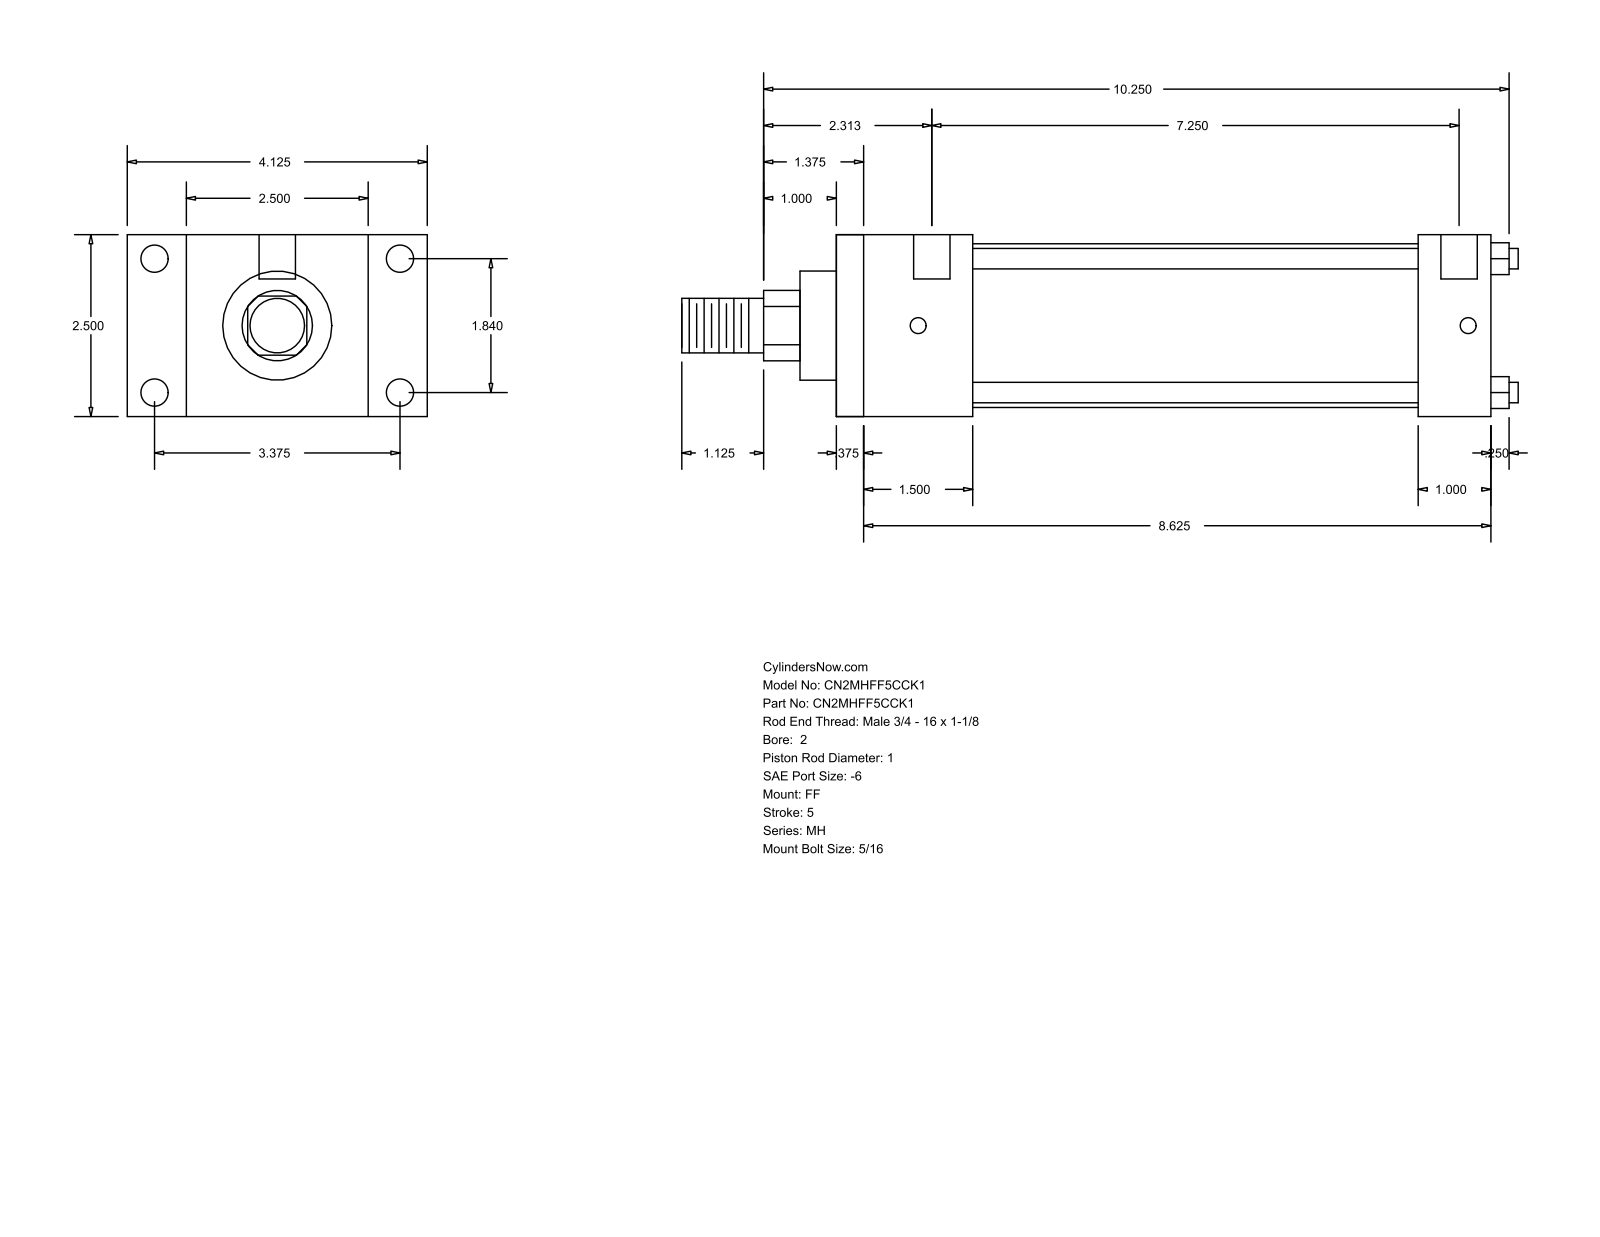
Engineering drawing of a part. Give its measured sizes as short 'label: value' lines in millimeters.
name: MH_FF__0200_1
written by: GSSL Pune (CONFIG_CONTROL_DESIGN)
unit: mm
bodies: 0 solids, 92 faces (64 planar, 28 cylindrical, 0 other)
size: 292.1 × 104.78 × 63.5
holes: 4× ⌀5.56, 4× ⌀9.53, 2× ⌀12.7
bosses: 4× ⌀7.14, 1× ⌀57.15, 1× ⌀38.1, 1× ⌀25.4, 1× ⌀19.05
rounds: 1× R12.29
face distances: 63.5, 228.6, 9.52, 219.08, 20.64, 25.4, 47.63, 203.2, 38.11, 193.68
hole spacings: 46.74, 85.72, 97.63, 192.08, 3.17, 4.76, 184.15, 187.32
